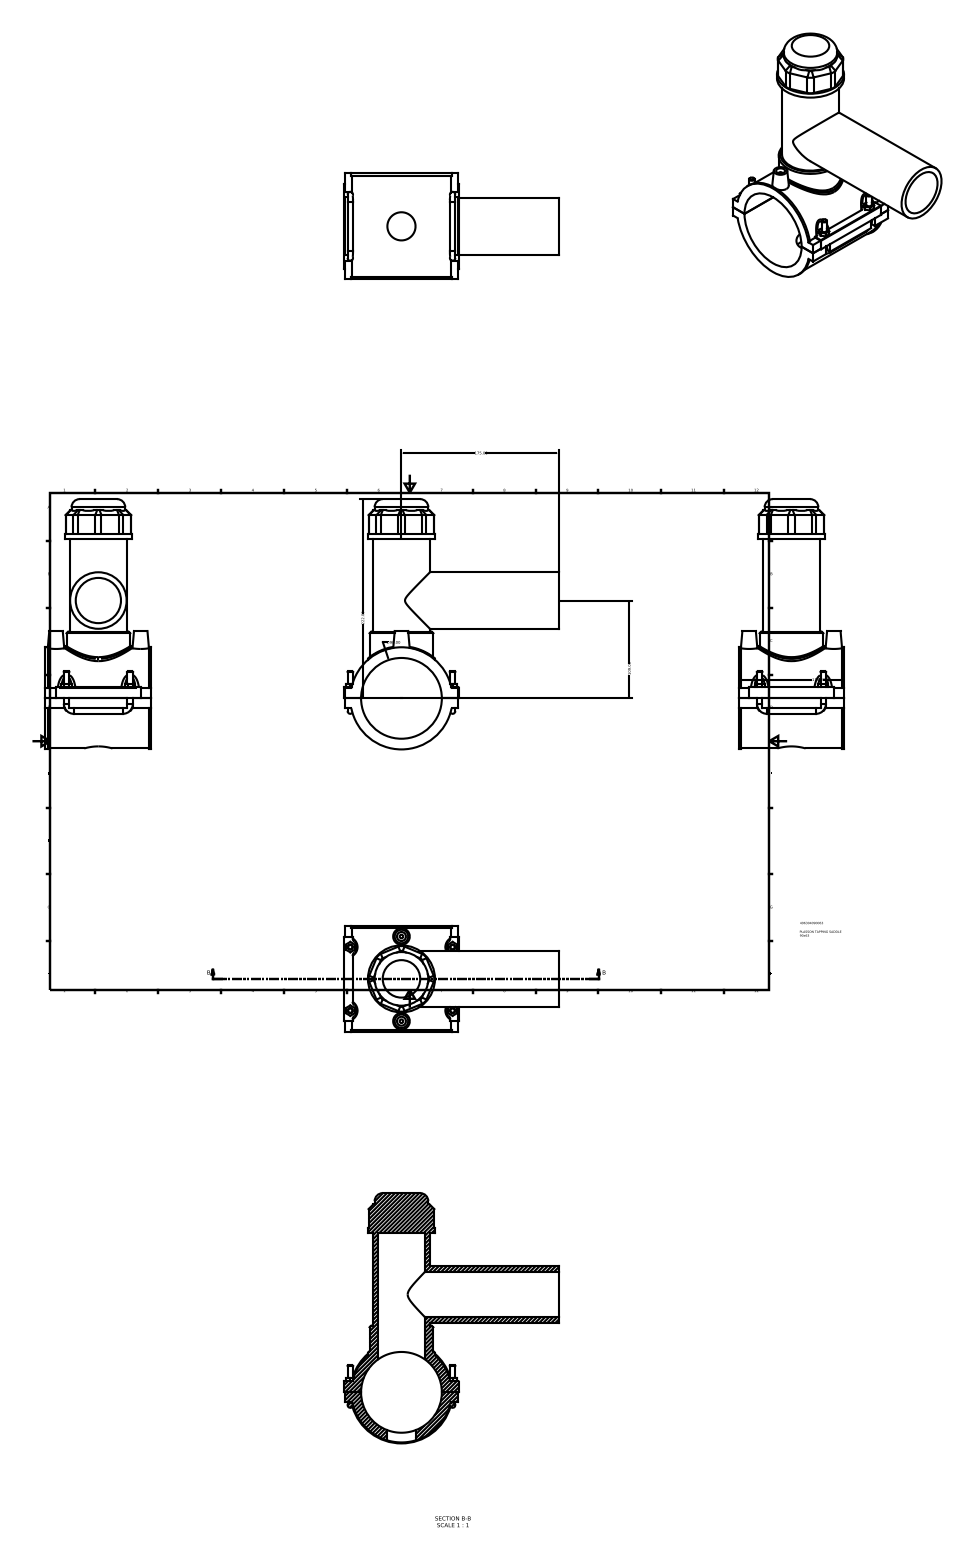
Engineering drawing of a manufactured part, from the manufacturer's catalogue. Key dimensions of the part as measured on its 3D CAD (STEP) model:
Part name (STEP PRODUCT): 496304090063
STEP written by: Autodesk Inventor 2015 (AUTOMOTIVE_DESIGN)
Units: millimetres
Bodies: 1 solid, 212 faces (126 planar, 57 cylindrical, 29 other)
Overall size (bounding box): 278.92 × 239 × 118
Volume: 888 492 mm³ · Surface area: 212 576 mm²
Round holes (diameter × count): ⌀10 ×2, ⌀31.36 ×1, ⌀50.4 ×1, ⌀52.29 ×1, ⌀90 ×1
Round bosses / shafts (diameter × count): ⌀6 ×6, ⌀4 ×2, ⌀113.83 ×1, ⌀111.6 ×1, ⌀74.7 ×1, ⌀70.97 ×1, ⌀63.49 ×1, ⌀63 ×1
Partial cylindrical surfaces — rounded edges, fillets, slot ends (radius × count): R9 ×8, R3 ×4, R7.5 ×4, R0.5 ×1, R58.03 ×1
Main face-to-face distances: 118, 177.8, 177.7, 1, 127, 11.2, 11.3, 189, 23.5, 12.3
Hole centre spacings: 47.2, 94.4
